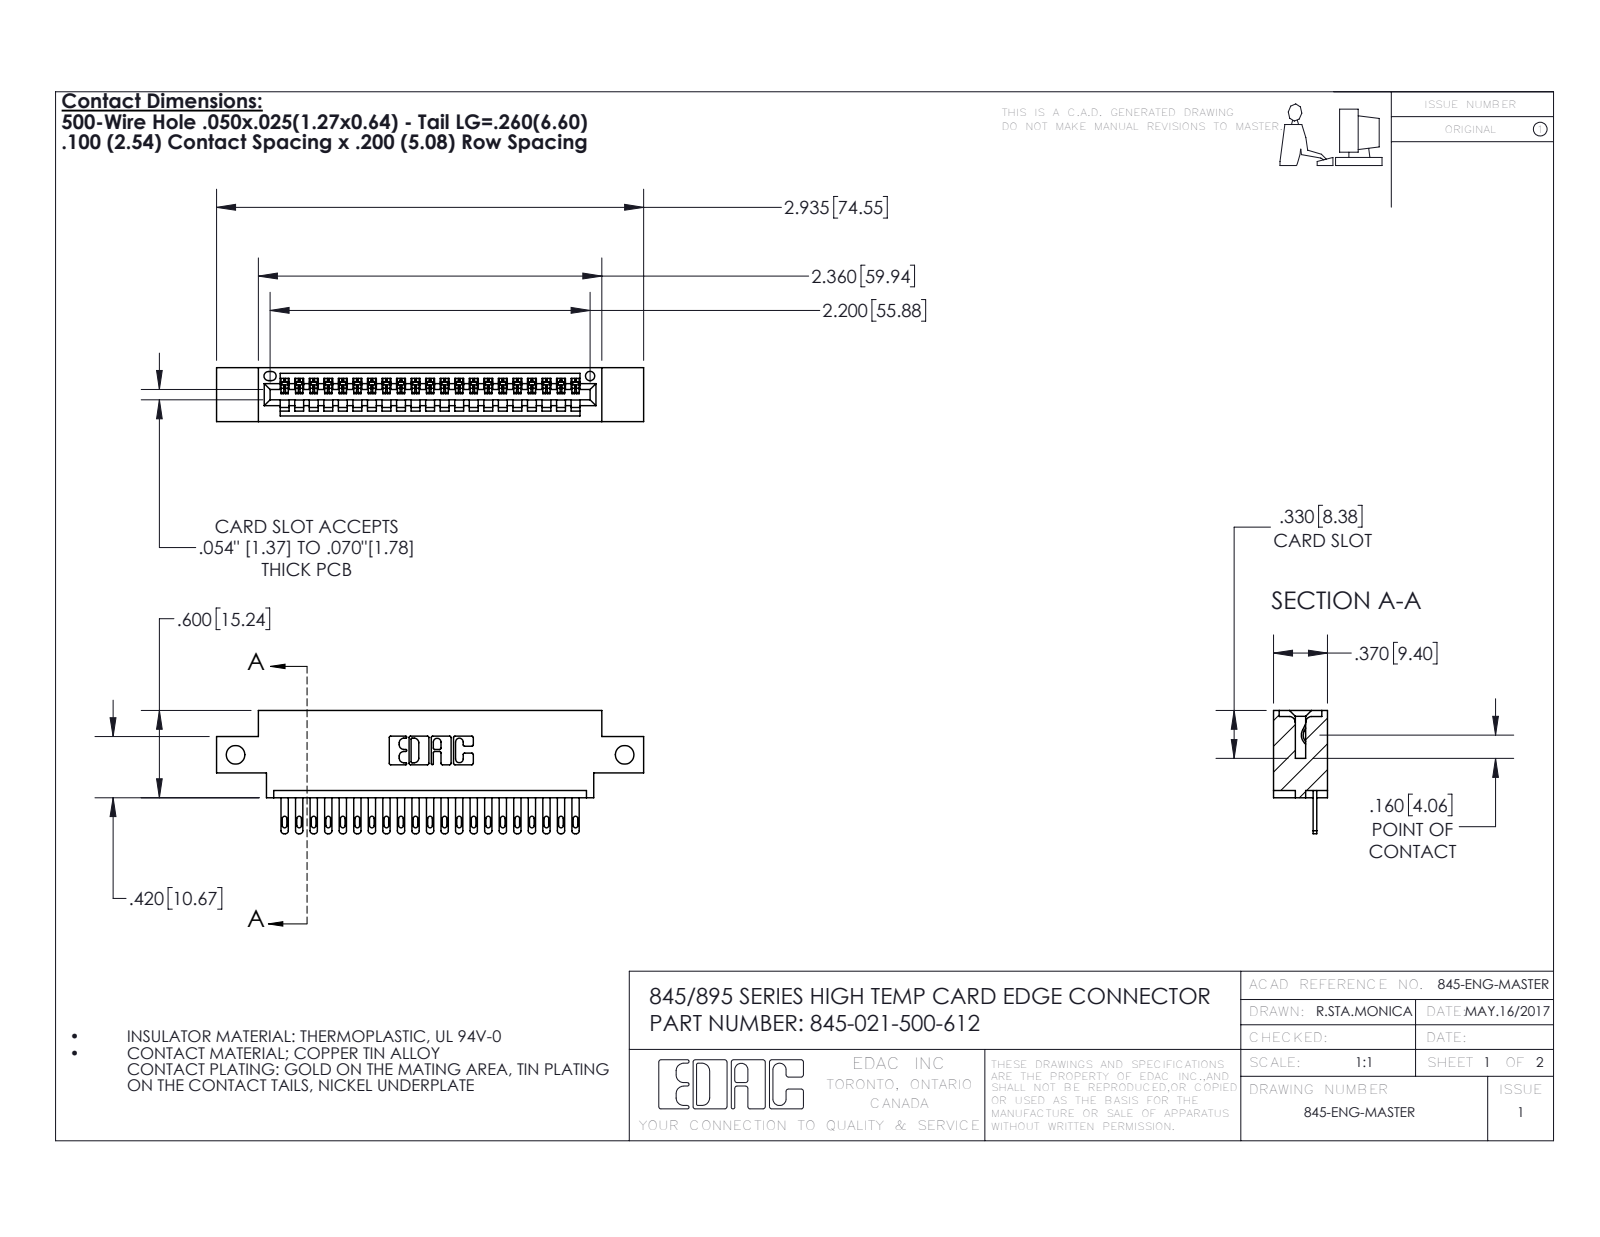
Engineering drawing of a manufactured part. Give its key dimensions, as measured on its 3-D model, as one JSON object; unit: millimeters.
{"part_name": "345-021-500-612; 345-292-001_345-293-100; 345 Part_0.170 Offset - Side Mount", "step_written_by": "SolidWorks 2016 (CONFIG_CONTROL_DESIGN)", "units": "millimeters", "bodies": {"solids": 22, "faces": 1264, "planar": 798, "cylindrical": 466, "other": 0}, "overall_size": [74.5, 21.5, 9.4], "volume_mm3": 6720, "surface_area_mm2": 8677, "round_holes": [[3.3, 2], [1.6, 1]], "partial_cylinders_radius": [[0.2, 42], [0.4, 42], [0.5, 42], [0.3, 22], [0.2, 6], [0.8, 6], [0.7, 3], [0.8, 2]], "face_to_face_distances": [7.6, 1.8, 9.4, 5.1, 2.5, 6.9, 0.6, 5.7, 4.4, 3.8], "hole_center_spacings": [67.9]}
